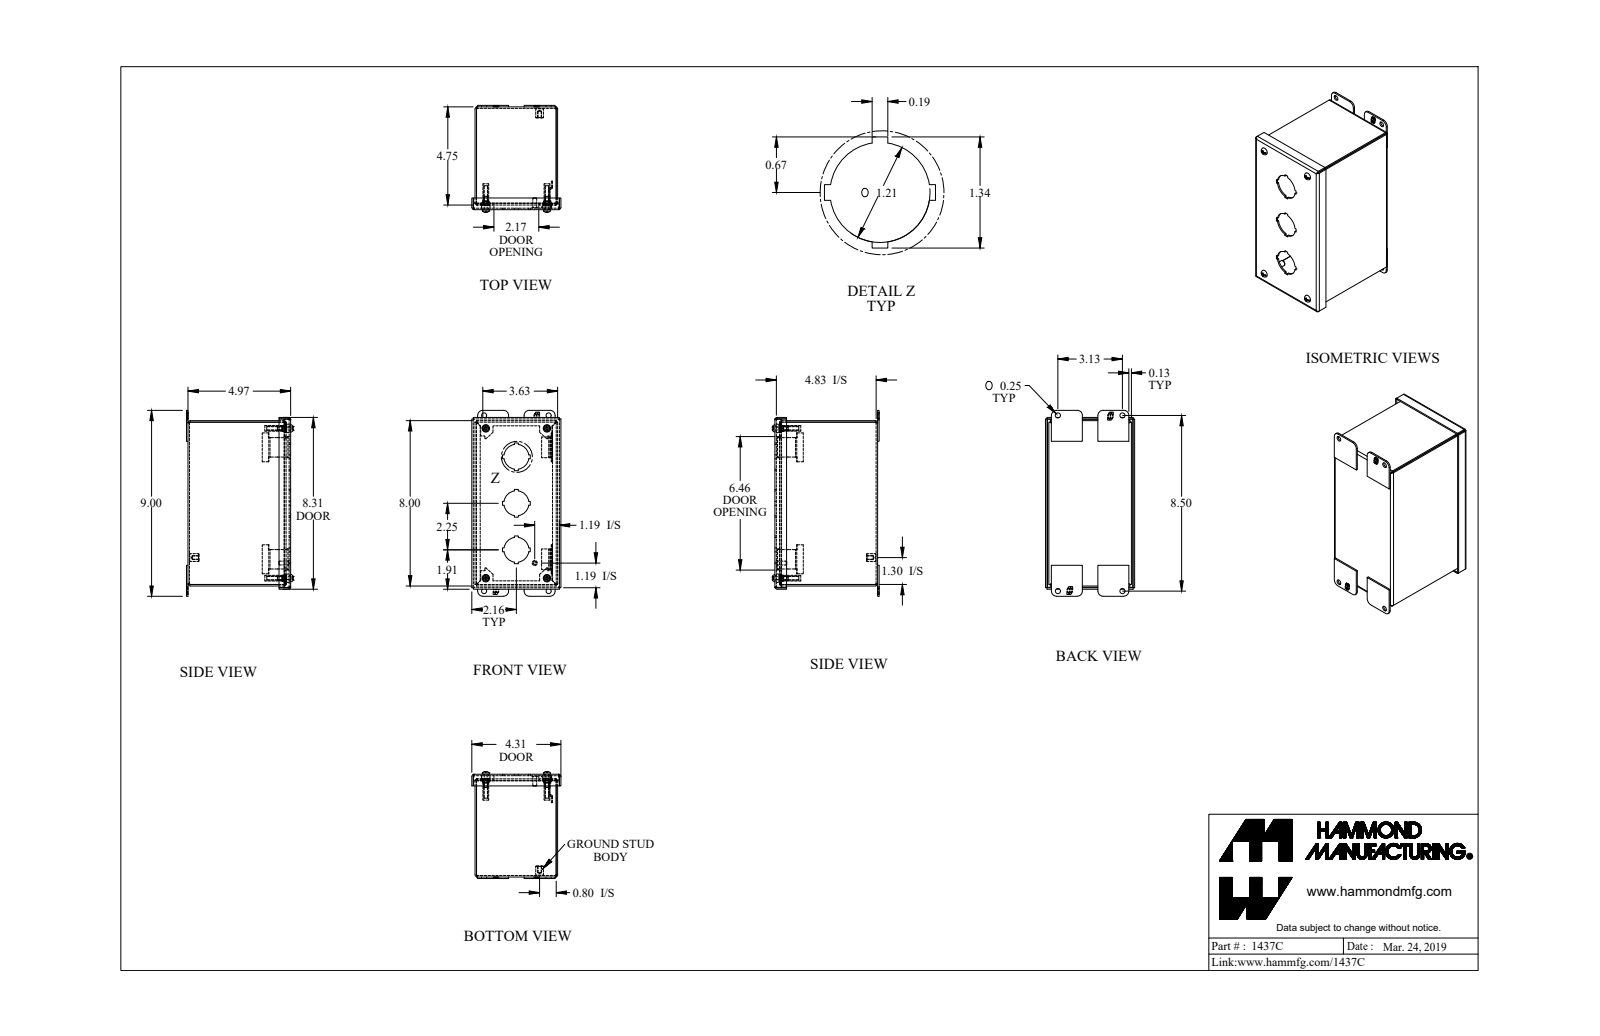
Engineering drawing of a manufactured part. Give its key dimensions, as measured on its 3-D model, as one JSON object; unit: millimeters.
{"part_name": "1437C_Default", "step_written_by": "SolidWorks 2019 (CONFIG_CONTROL_DESIGN)", "units": "millimeters", "bodies": {"solids": 23, "faces": 763, "planar": 535, "cylindrical": 172, "other": 56}, "overall_size": [228.6, 131.3, 109.5], "volume_mm3": 278900, "surface_area_mm2": 293500, "round_holes": [[6.4, 8], [4, 4], [10.3, 4], [30.7, 3], [4, 1]], "round_bosses_or_shafts": [[9.9, 4], [7, 4], [4.8, 4], [3.8, 4], [9.5, 1], [6.4, 1], [4.8, 1]], "partial_cylinders_radius": [[0.9, 12], [2.7, 12], [6.4, 8], [0.7, 4], [2.2, 4], [3.2, 4], [4.1, 4], [4.3, 4]], "face_to_face_distances": [1.8, 99.8, 124.5, 126.3, 101.6, 97.9, 201.4, 122.6, 4, 203.2], "hole_center_spacings": [16, 99.5, 153.9, 184.2, 200.1, 214.5, 51.3, 78.9]}
